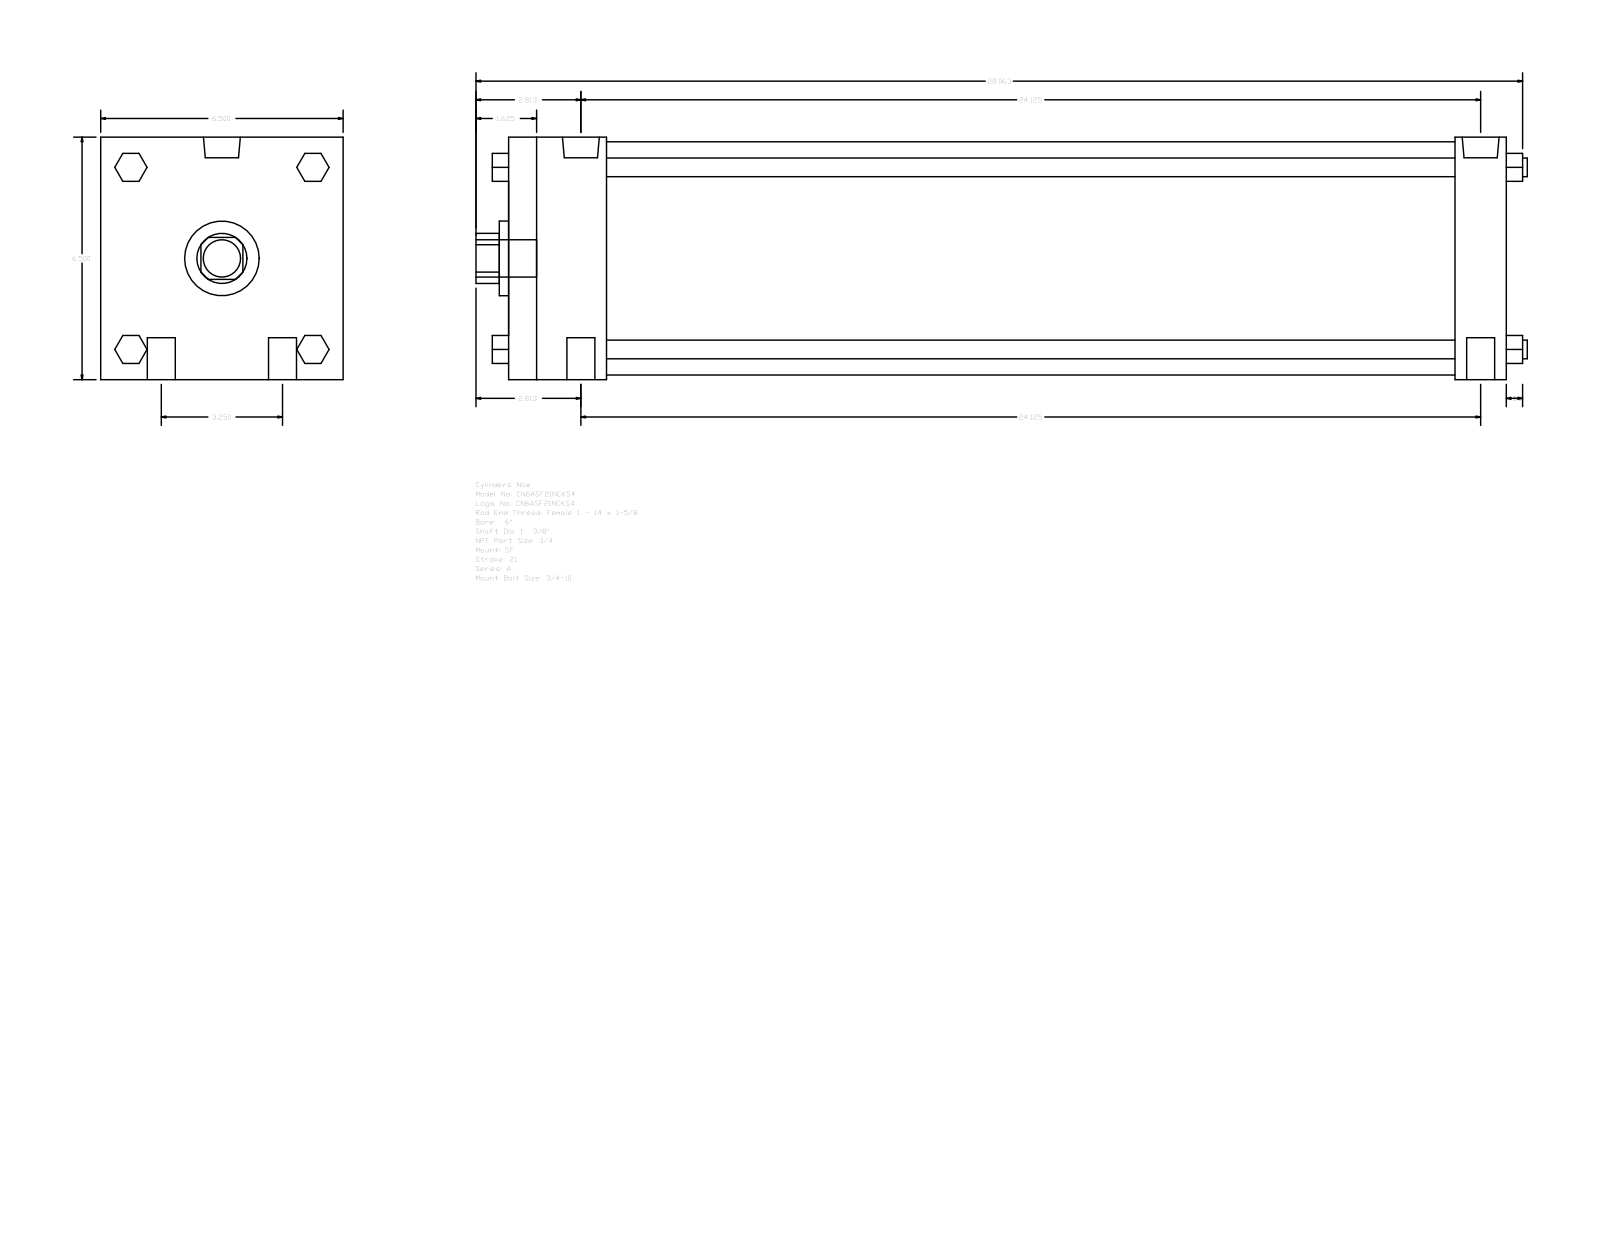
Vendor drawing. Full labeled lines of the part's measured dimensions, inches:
Part name (STEP PRODUCT): A_SF__0600_1.375
STEP written by: GSSL Pune (CONFIG_CONTROL_DESIGN)
Units: inches
Bodies: 0 solids, 124 faces (94 planar, 30 cylindrical, 0 other)
Overall size (bounding box): 28.187 × 6.5 × 6.5
Round holes (diameter × count): ⌀1.375 ×1, ⌀2 ×1, ⌀6.25 ×1
Round bosses / shafts (diameter × count): ⌀0.75 ×4, ⌀0.5 ×4, ⌀0.989 ×2, ⌀0.594 ×2, ⌀1 ×1
Partial cylindrical surfaces — rounded edges, fillets, slot ends (radius × count): R0.672 ×1
Main face-to-face distances: 6.5, 26.75, 25.375, 1.375, 2.625, 22.75, 24.125, 0.75, 2.44, 4.226
